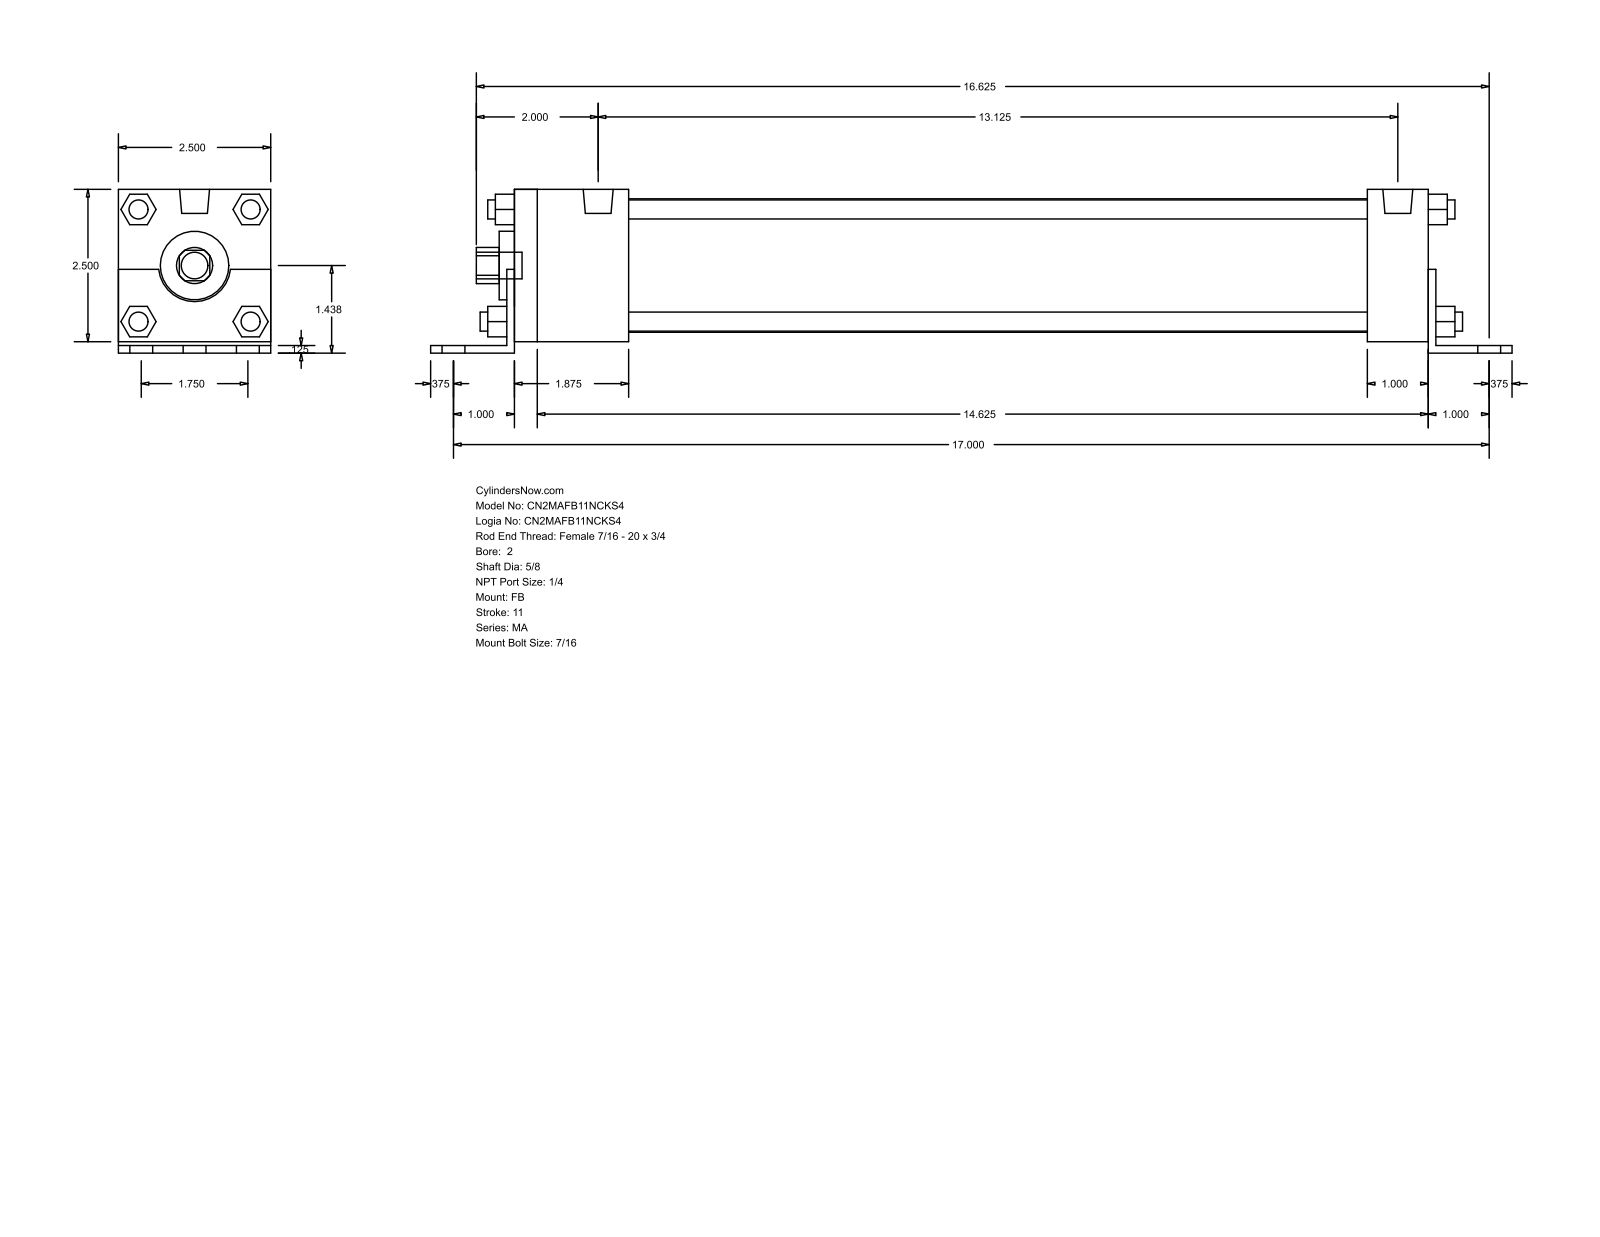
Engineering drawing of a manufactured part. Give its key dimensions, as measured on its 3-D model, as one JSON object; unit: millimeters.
{"part_name": "MA_FB__0200_0.625", "step_written_by": "GSSL Pune (CONFIG_CONTROL_DESIGN)", "units": "millimeters", "bodies": {"solids": 0, "faces": 140, "planar": 105, "cylindrical": 35, "other": 0}, "overall_size": [450.85, 68.26, 63.5], "round_holes": [[15.88, 1], [28.57, 1], [55.63, 1]], "round_bosses_or_shafts": [[7.94, 8], [11.11, 7], [12.49, 2]], "partial_cylinders_radius": [[7.54, 1], [15.05, 1]], "face_to_face_distances": [63.5, 3.17, 4.76, 68.26, 1.59, 65.09, 381, 387.35, 3.18, 384.17]}
